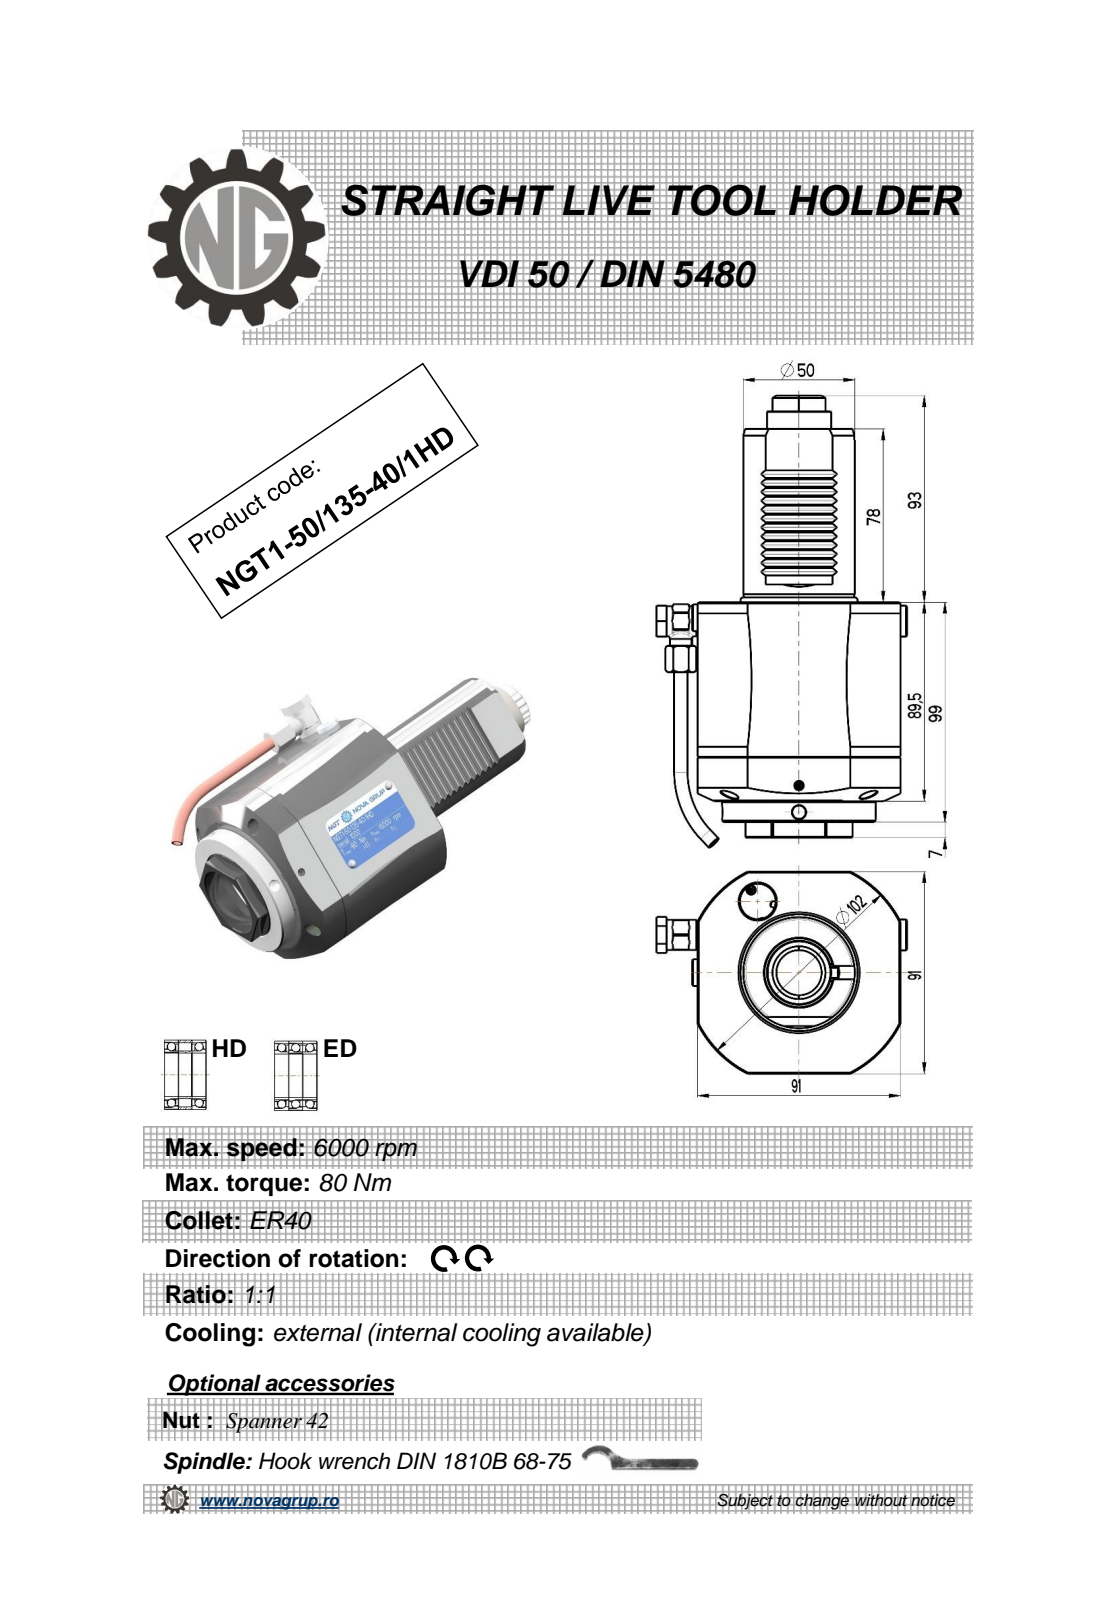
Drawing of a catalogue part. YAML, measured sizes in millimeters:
part_name: "NGT1_50_135_40_3HD"
step_written_by: "PRO/ENGINEER BY PARAMETRIC TECHNOLOGY CORPORATION, 2010280 (CONFIG_CONTROL_DESIGN)"
units: millimeters
bodies: {solids: 1, faces: 547, planar: 178, cylindrical: 197, other: 172}
overall_size: [203.44, 112.4, 91]
volume: 843702
surface_area: 68206
round_holes:
  - {diameter: 4, count: 3}
  - {diameter: 6, count: 2}
  - {diameter: 3, count: 1}
  - {diameter: 6.2, count: 1}
  - {diameter: 9, count: 1}
  - {diameter: 10, count: 1}
  - {diameter: 11, count: 1}
  - {diameter: 36.2, count: 1}
  - {diameter: 42, count: 1}
round_bosses_or_shafts:
  - {diameter: 6, count: 2}
  - {diameter: 69, count: 1}
  - {diameter: 50, count: 1}
  - {diameter: 28.8, count: 1}
  - {diameter: 14, count: 1}
  - {diameter: 13.6, count: 1}
  - {diameter: 13, count: 1}
  - {diameter: 12, count: 1}
partial_cylinders:
  - {radius: 3.04, count: 36}
  - {radius: 0.3, count: 12}
  - {radius: 0.41, count: 6}
  - {radius: 0.5, count: 4}
  - {radius: 6.25, count: 1}
  - {radius: 7.7, count: 1}
  - {radius: 10.56, count: 1}
  - {radius: 10.75, count: 1}
face_to_face_distances: [91, 89.5, 9.5, 99, 2.83, 78, 177, 167.5, 14.14, 25.5]
hole_center_spacings: [0.4, 55.66, 56.04, 87.66]
